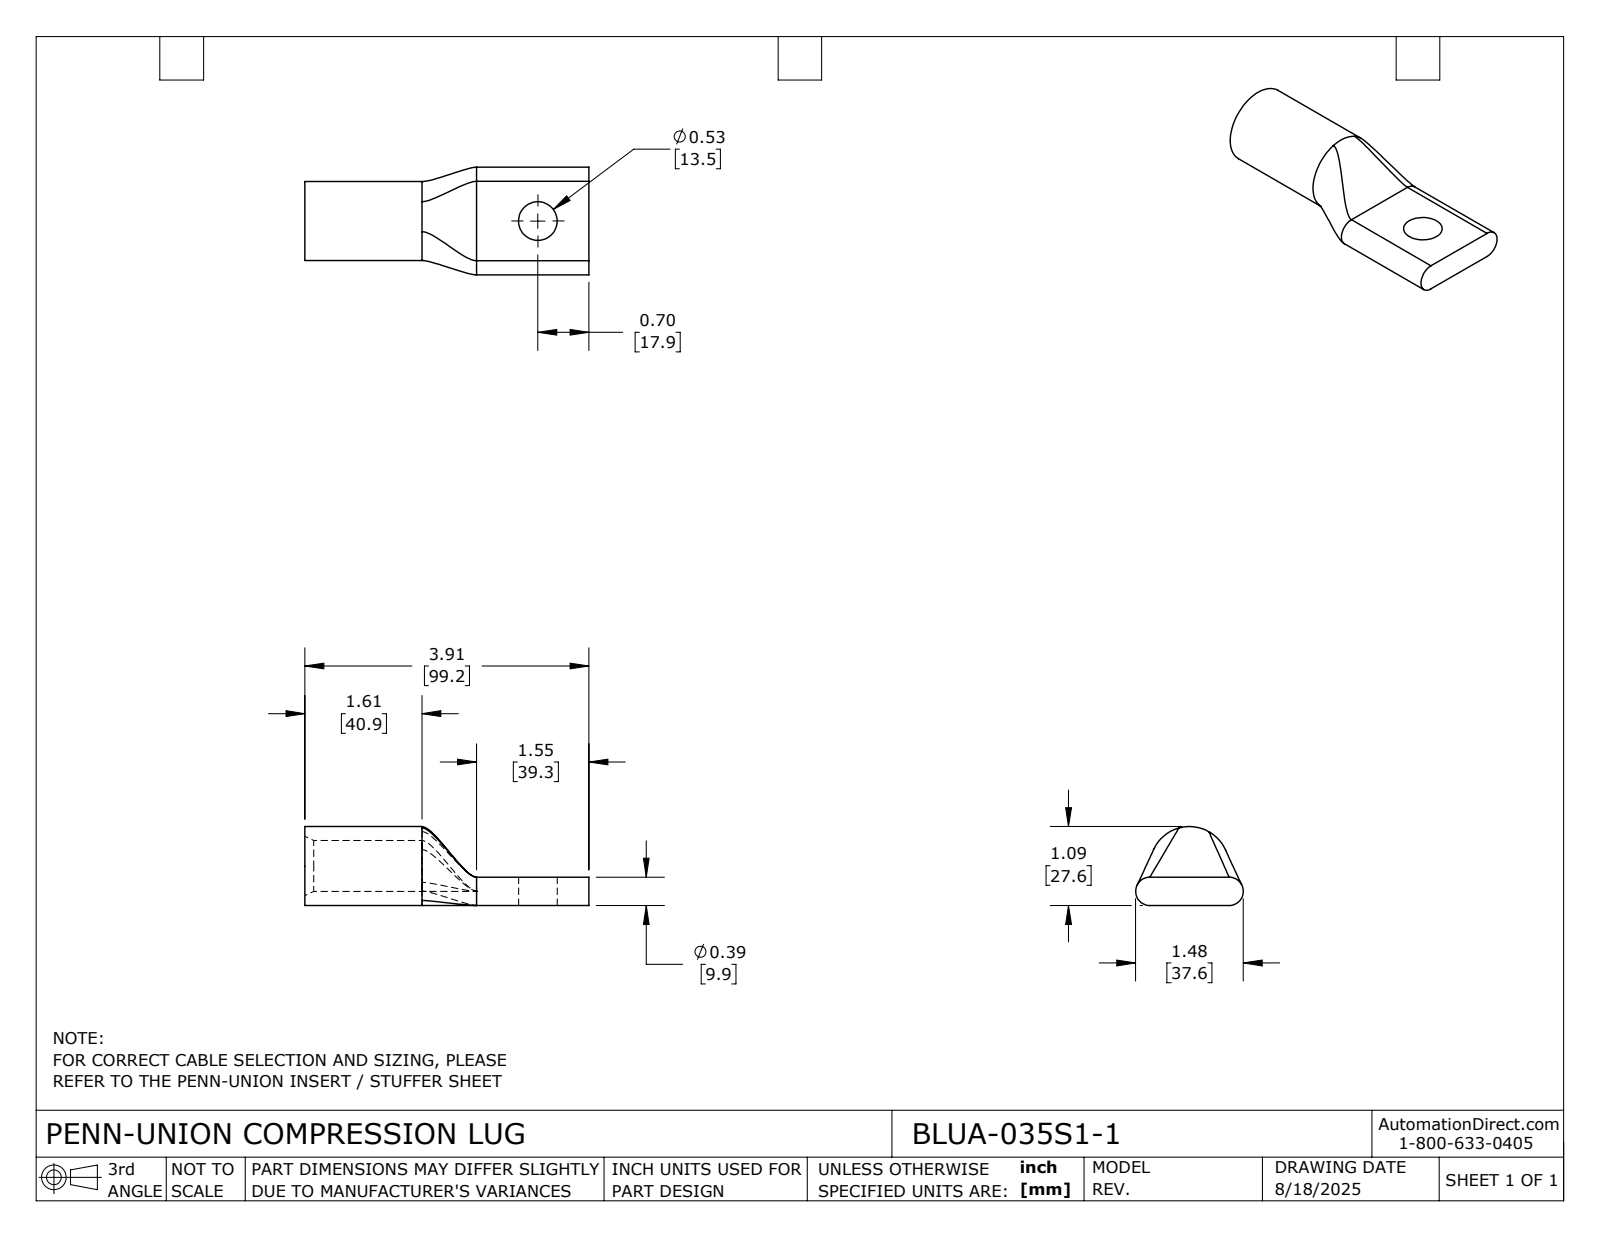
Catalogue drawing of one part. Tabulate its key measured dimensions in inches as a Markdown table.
| quantity | value |
| --- | --- |
| part name | BLUA-035S1-1 |
| STEP written by | SolidWorks 2024 (CONFIG_CONTROL_DESIGN) |
| units | inches |
| bodies | 1 solid, 24 faces (5 planar, 9 cylindrical, 10 other) |
| overall size | 3.906 × 1.48 × 1.085 |
| volume | 2.02 in³ |
| surface area | 20.17 in² |
| round holes (diameter × count) | 0.531 × 1, 0.7 × 1 |
| round bosses / shafts (diameter × count) | 1.085 × 1 |
| partial cylindrical surfaces (radius × count) | 0.195 × 2 |
| main face-to-face distances | 0.39, 3.906, 2.359, 1.547 |
